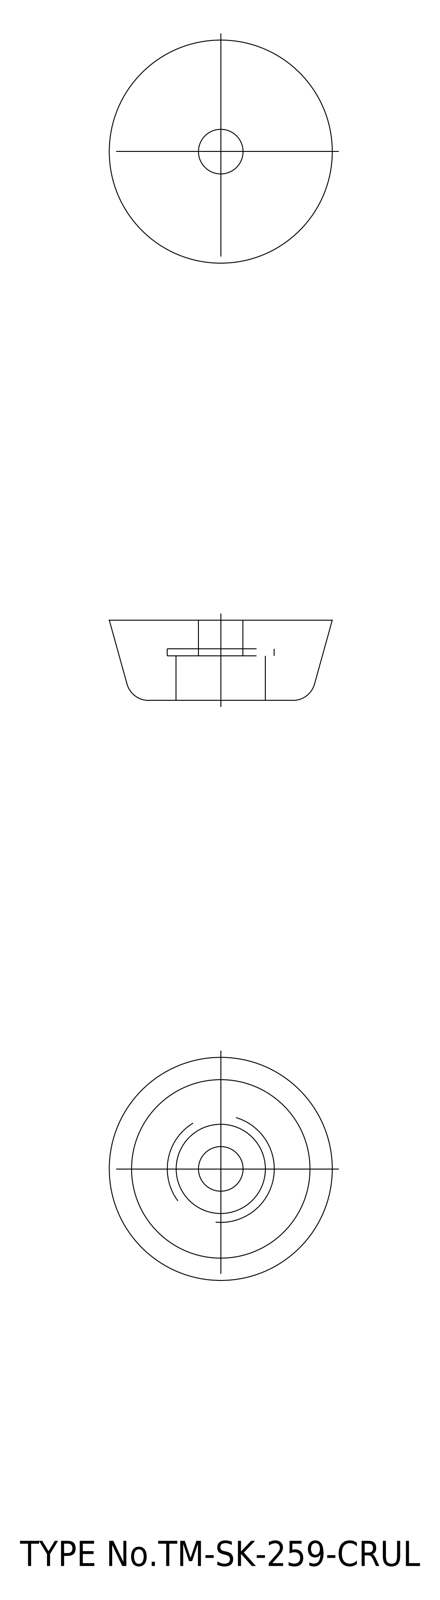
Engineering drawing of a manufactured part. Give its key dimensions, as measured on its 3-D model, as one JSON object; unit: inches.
{"part_name": "washer; rubber foot", "step_written_by": "spGate 15.6.1 (AUTOMOTIVE_DESIGN)", "units": "inches", "bodies": {"solids": 2, "faces": 20, "planar": 6, "cylindrical": 10, "other": 4}, "overall_size": [0.984, 0.984, 0.354], "volume_in3": 0.19, "surface_area_in2": 3.01, "round_holes": [[0.197, 1], [0.394, 1], [0.472, 1]], "face_to_face_distances": [0.126, 0.228, 0.354, 0.197, 0.031, 0.157]}
